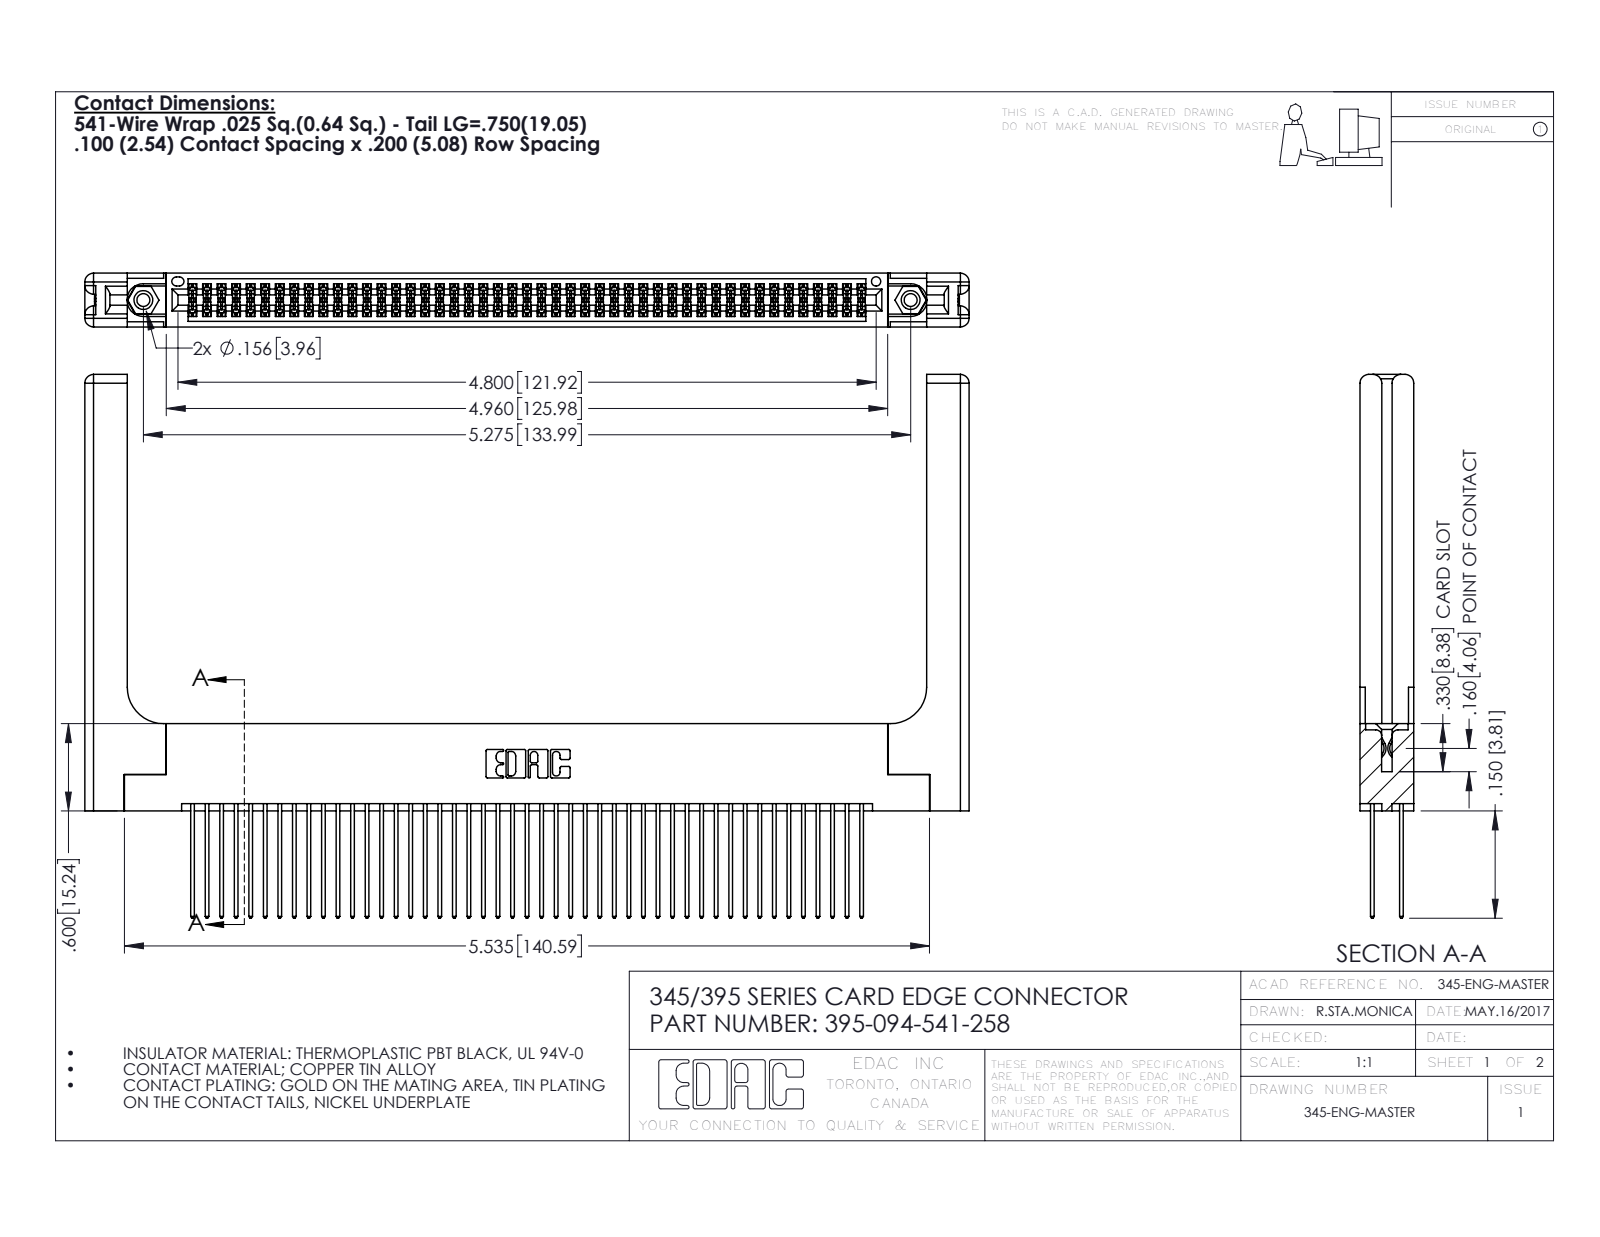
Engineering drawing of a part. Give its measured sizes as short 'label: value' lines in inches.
name: 345-220-058_345-220-058; 345-292-001_345-293-141; 345-250-001_345-250-001-102; 345 Part_Flush Mounting Lugs - 0.156 Dia-TH (+1 more)
written by: SolidWorks 2016 (CONFIG_CONTROL_DESIGN)
unit: in
bodies: 99 solids, 5082 faces (3330 planar, 1692 cylindrical, 60 other)
size: 6.079 × 3.737 × 0.37
volume: 1.468 in³; area: 47.63 in²
holes: 2× ⌀0.089, 2× ⌀0.125, 2× ⌀0.156, 1× ⌀0.064
bosses: 2× ⌀0.155
rounds: 141× R0.006, 94× R0.01, 22× R0.01, 16× R0.06, 6× R0.007, 6× R0.031, 3× R0.026, 2× R0.014
face distances: 0.072, 0.298, 0.2, 0.37, 0.098, 0.272, 0.025, 0.225, 0.175, 0.148
hole spacings: 0.27, 5.039, 5.275
